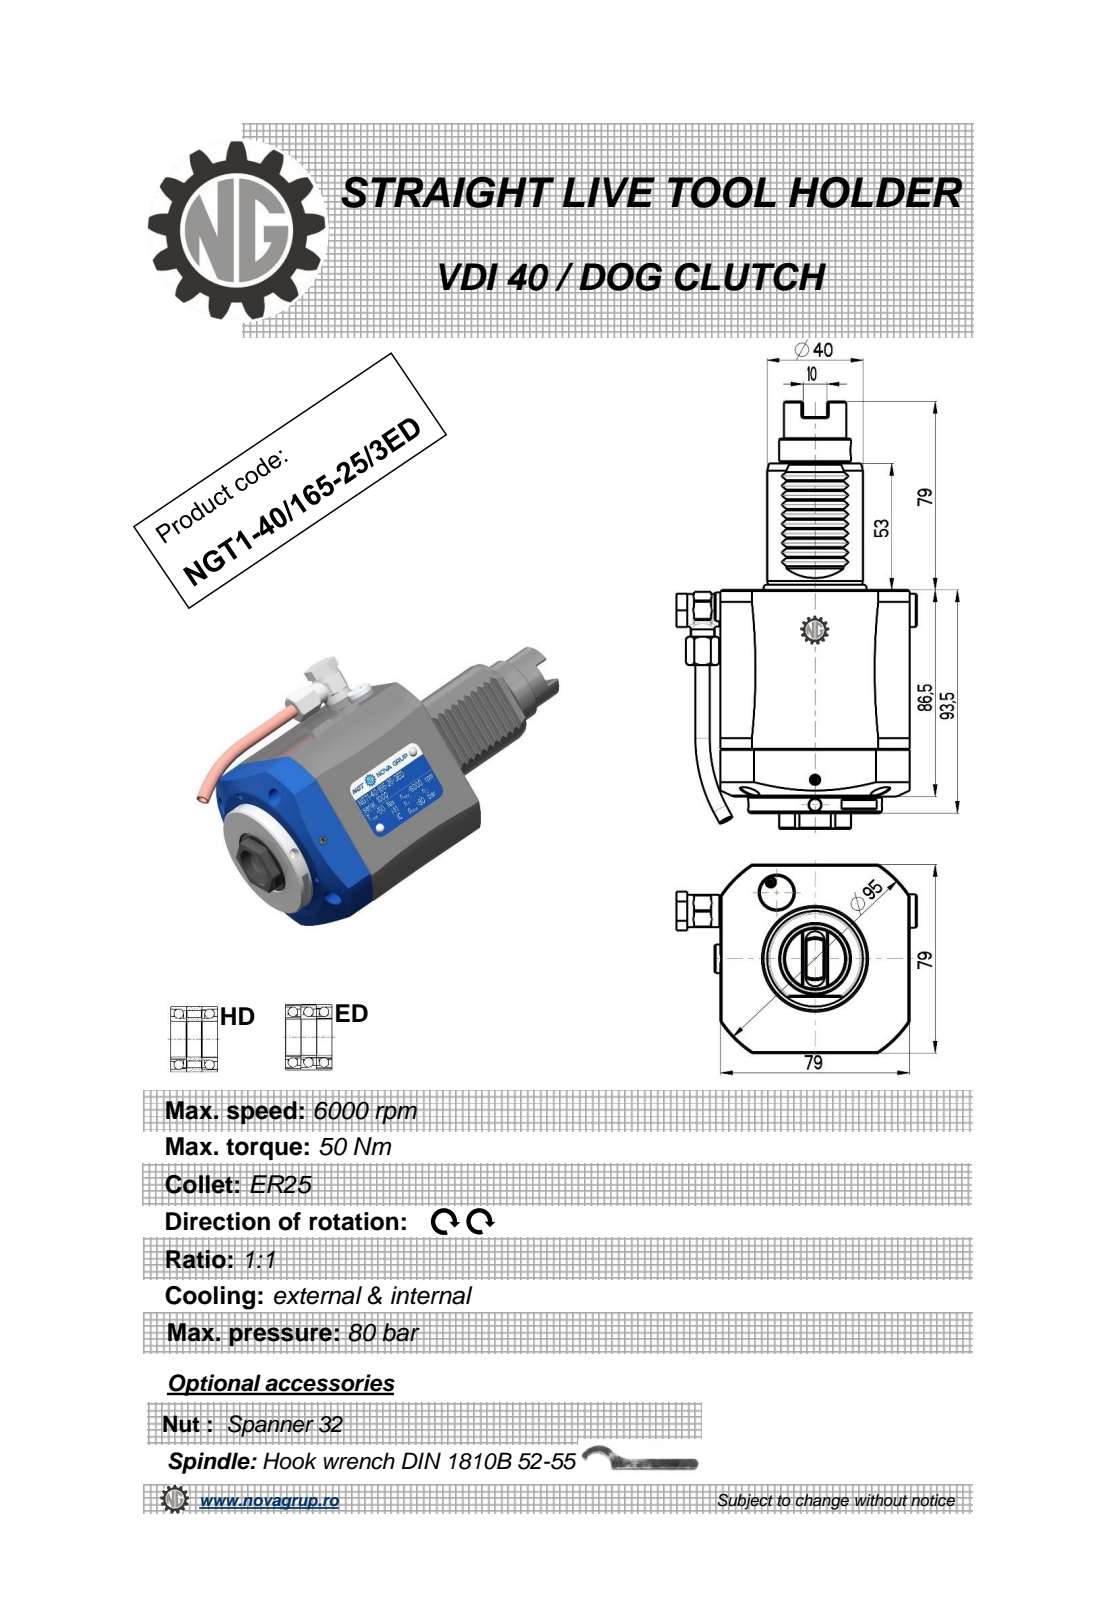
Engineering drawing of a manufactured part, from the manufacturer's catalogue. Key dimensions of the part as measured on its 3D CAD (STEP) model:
Part name (STEP PRODUCT): NGT1_40_165_25_3HD
STEP written by: PRO/ENGINEER BY PARAMETRIC TECHNOLOGY CORPORATION, 2010280 (CONFIG_CONTROL_DESIGN)
Units: millimetres
Bodies: 2 solids, 395 faces (155 planar, 109 cylindrical, 131 other)
Overall size (bounding box): 179 × 100.4 × 79
Volume: 603 161 mm³ · Surface area: 54 369 mm²
Round holes (diameter × count): ⌀4 ×3, ⌀5 ×2, ⌀3 ×1, ⌀6 ×1, ⌀6.2 ×1, ⌀9 ×1, ⌀10 ×1, ⌀11 ×1, ⌀18 ×1, ⌀26.5 ×1
Round bosses / shafts (diameter × count): ⌀56 ×1, ⌀40 ×1, ⌀30 ×1, ⌀26 ×1, ⌀14 ×1, ⌀13.6 ×1, ⌀13 ×1, ⌀12 ×1
Partial cylindrical surfaces — rounded edges, fillets, slot ends (radius × count): R0.3 ×10, R0.41 ×6, R0.5 ×6, R7.7 ×1, R47 ×1, R47.5 ×1
Main face-to-face distances: 79, 86.5, 7, 93.5, 2.83, 53, 139.5, 146.5, 6.5, 8.48
Hole centre spacings: 0.4, 51.08, 51.45, 83.92
